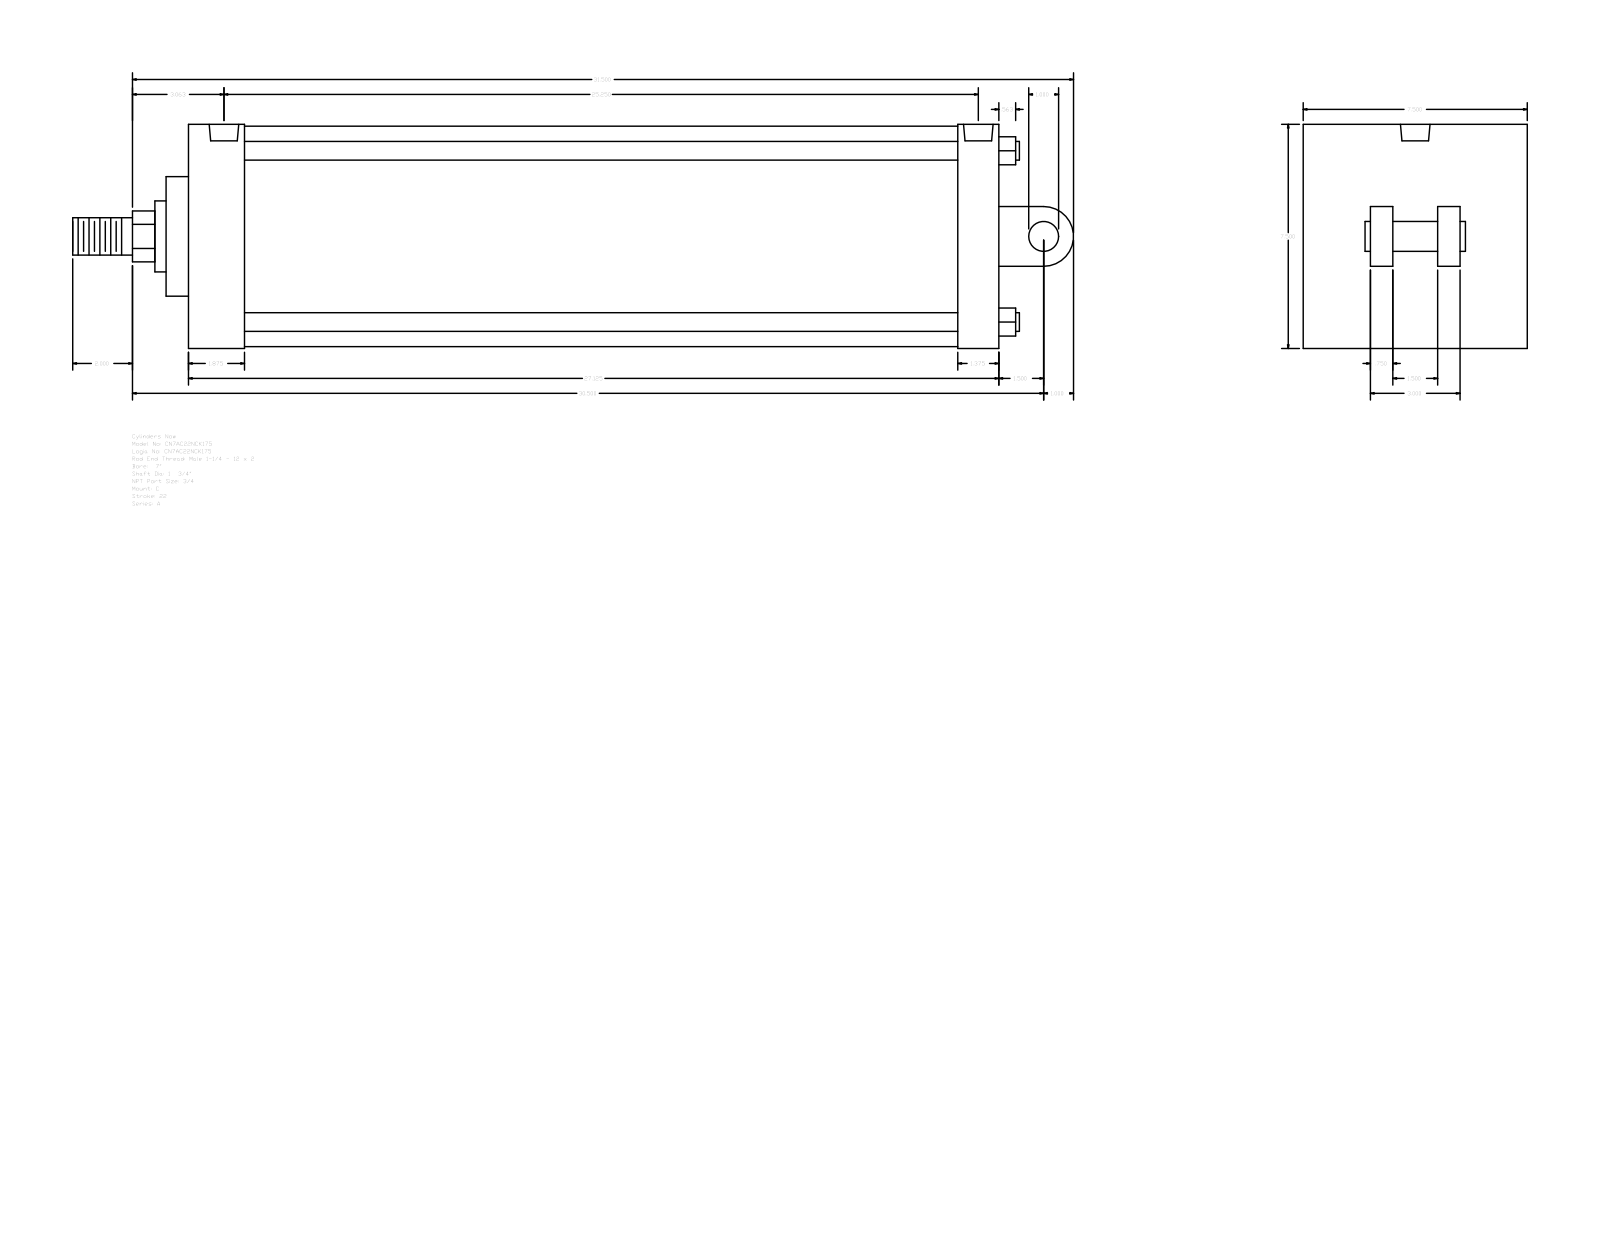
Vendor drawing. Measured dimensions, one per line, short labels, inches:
name: A_C__0700_1.75
written by: GSSL Pune (CONFIG_CONTROL_DESIGN)
unit: in
bodies: 0 solids, 104 faces (75 planar, 29 cylindrical, 0 other)
size: 33.5 × 7.5 × 7.5
holes: 4× ⌀0.594, 2× ⌀0.989
bosses: 4× ⌀0.625, 1× ⌀7.375, 1× ⌀2.375, 1× ⌀1.75, 1× ⌀1.25, 1× ⌀1
rounds: 1× R0.852, 1× R1
face distances: 7.5, 27.125, 0.75, 3, 2.25, 5.75, 1.75, 2.75, 1.875, 25.25
hole spacings: 0.219, 24.812, 25.031, 25.25
